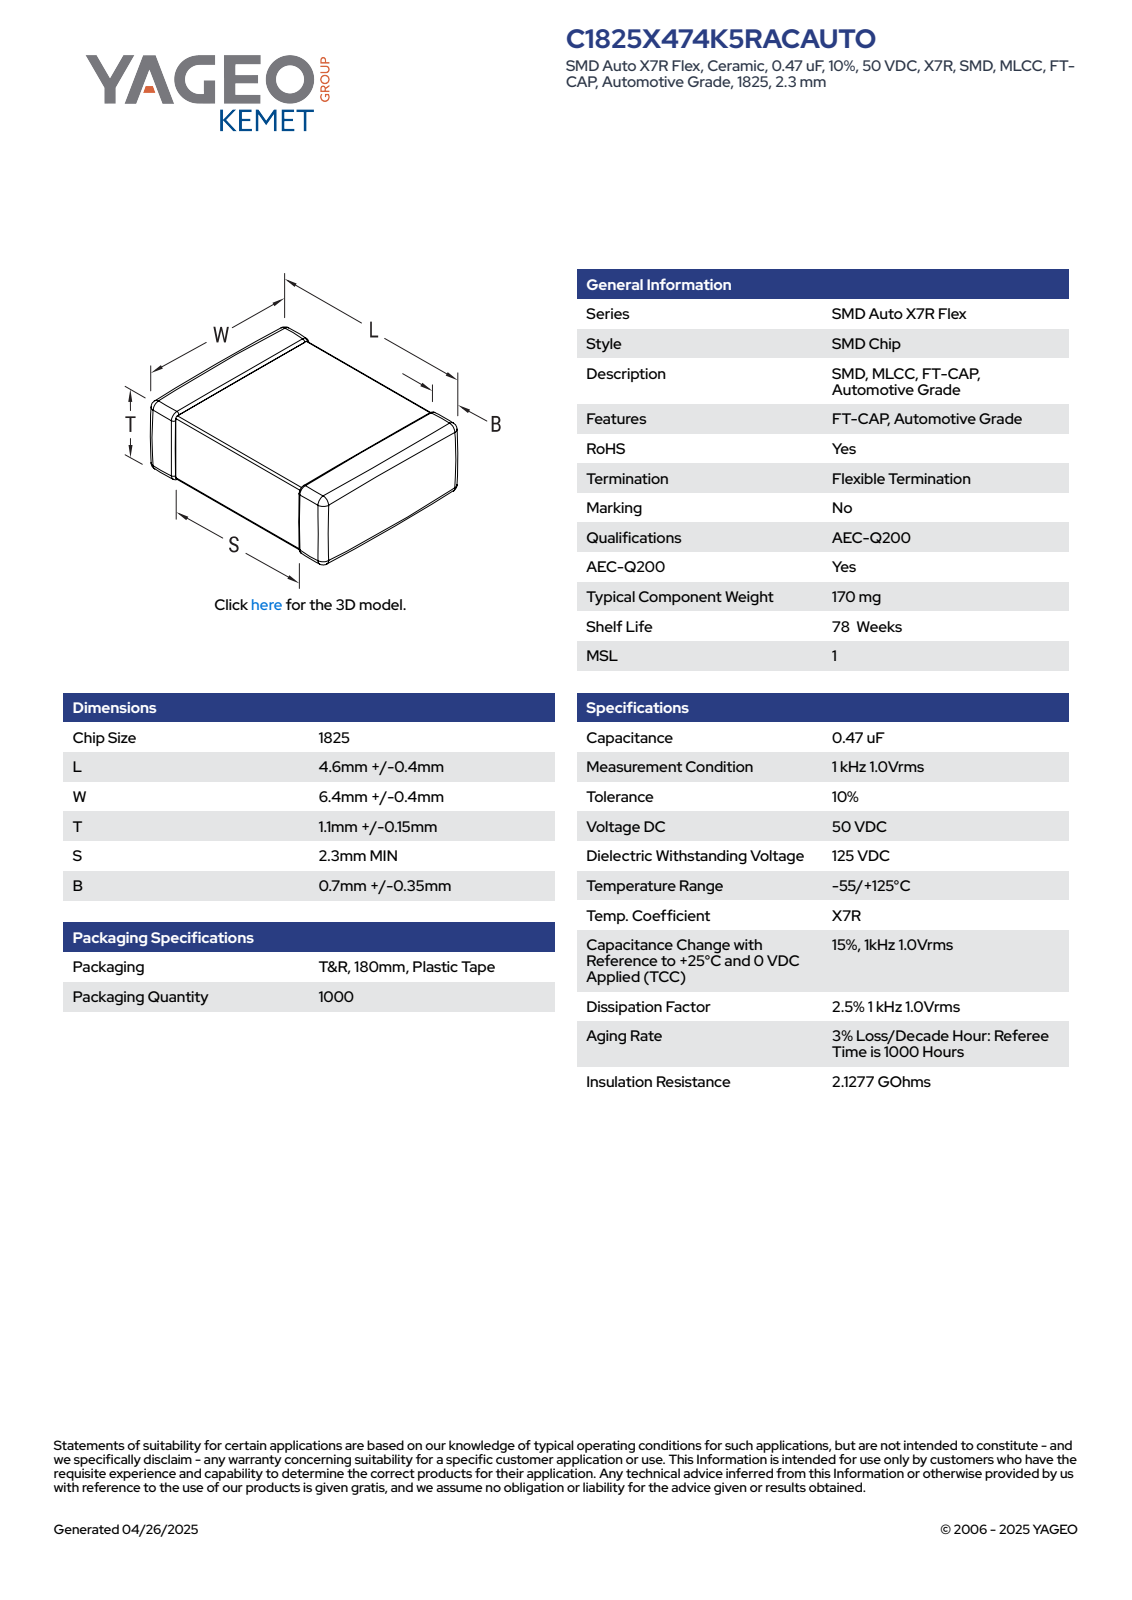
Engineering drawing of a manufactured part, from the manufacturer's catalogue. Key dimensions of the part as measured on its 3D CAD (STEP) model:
Part name (STEP PRODUCT): CCS_CCSTDNOS_1825_L5W6.8T1.25B1.05
STEP written by: SolidWorks 2014 (AUTOMOTIVE_DESIGN)
Units: millimetres
Bodies: 4 solids, 121 faces (71 planar, 34 cylindrical, 16 other)
Overall size (bounding box): 6.8 × 5 × 1.25
Volume: 36 mm³ · Surface area: 94 mm²
Partial cylindrical surfaces — rounded edges, fillets, slot ends (radius × count): R0.14 ×24
Main face-to-face distances: 1.11, 0.97, 1.25, 5, 6.66, 6.52, 6.8, 3.54, 3.12, 0.36
